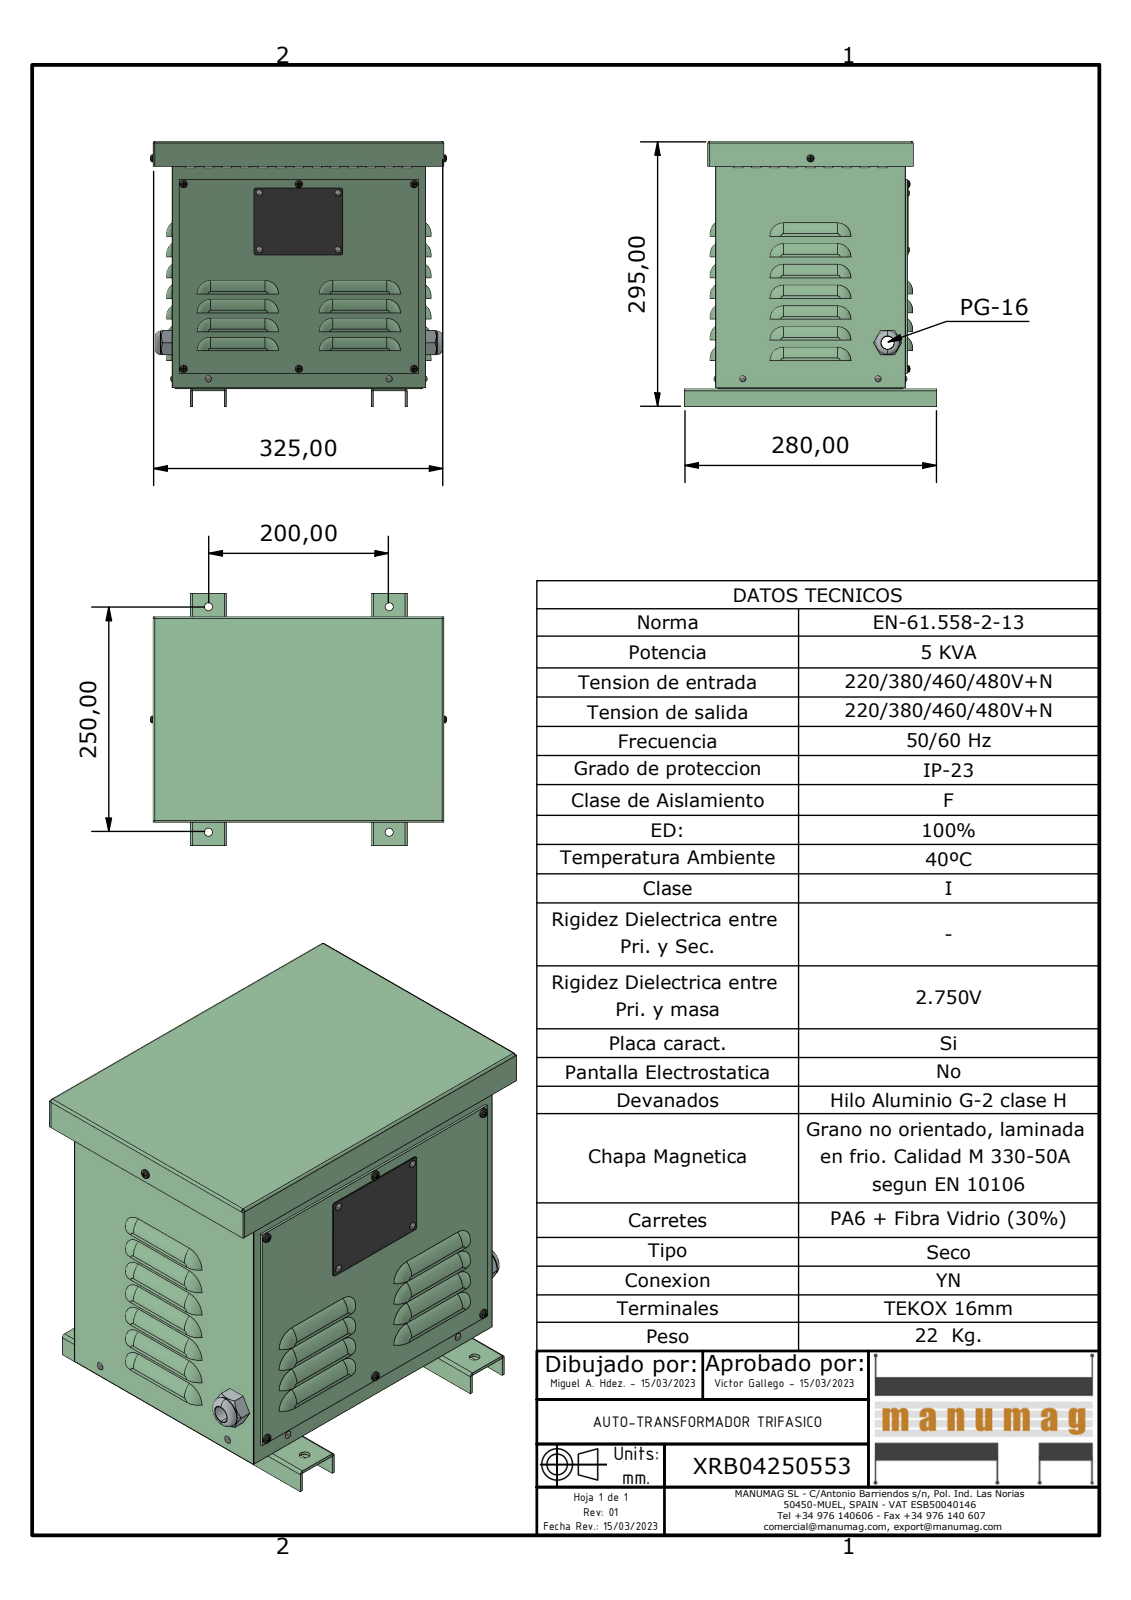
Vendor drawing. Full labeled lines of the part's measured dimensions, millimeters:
Part name (STEP PRODUCT): XRB04250553; JE003 - JE004 - JE005 EXPORT BASE; JE003 - JE004 - JE005 EXPORT PATA; JE003 - JE004 - JE005 EXPORT CUERPO (+6 more)
STEP written by: Autodesk Inventor 2023 (AUTOMOTIVE_DESIGN)
Units: millimetres
Bodies: 29 solids, 1436 faces (841 planar, 283 cylindrical, 312 other)
Overall size (bounding box): 328.13 × 294.5 × 280
Volume: 827 636 mm³ · Surface area: 1 061 000 mm²
Round holes (diameter × count): ⌀4.8 ×13, ⌀3 ×12, ⌀9 ×6, ⌀3.8 ×5, ⌀4 ×4, ⌀14 ×1, ⌀24 ×1
Round bosses / shafts (diameter × count): ⌀3.2 ×8, ⌀4 ×7, ⌀3.62 ×7, ⌀26 ×1, ⌀23 ×1, ⌀22.5 ×1
Partial cylindrical surfaces — rounded edges, fillets, slot ends (radius × count): R14 ×44, R4 ×25, R15 ×25, R0.5 ×9, R2 ×8, R4.5 ×8, R1.5 ×6, R1.5 ×4
Main face-to-face distances: 0.5, 2, 210.5, 280.5, 2.5, 1.5, 274.5, 272.5, 211, 213
Hole centre spacings: 127.5, 200, 241.42, 205, 29.62, 44.63, 47, 63
